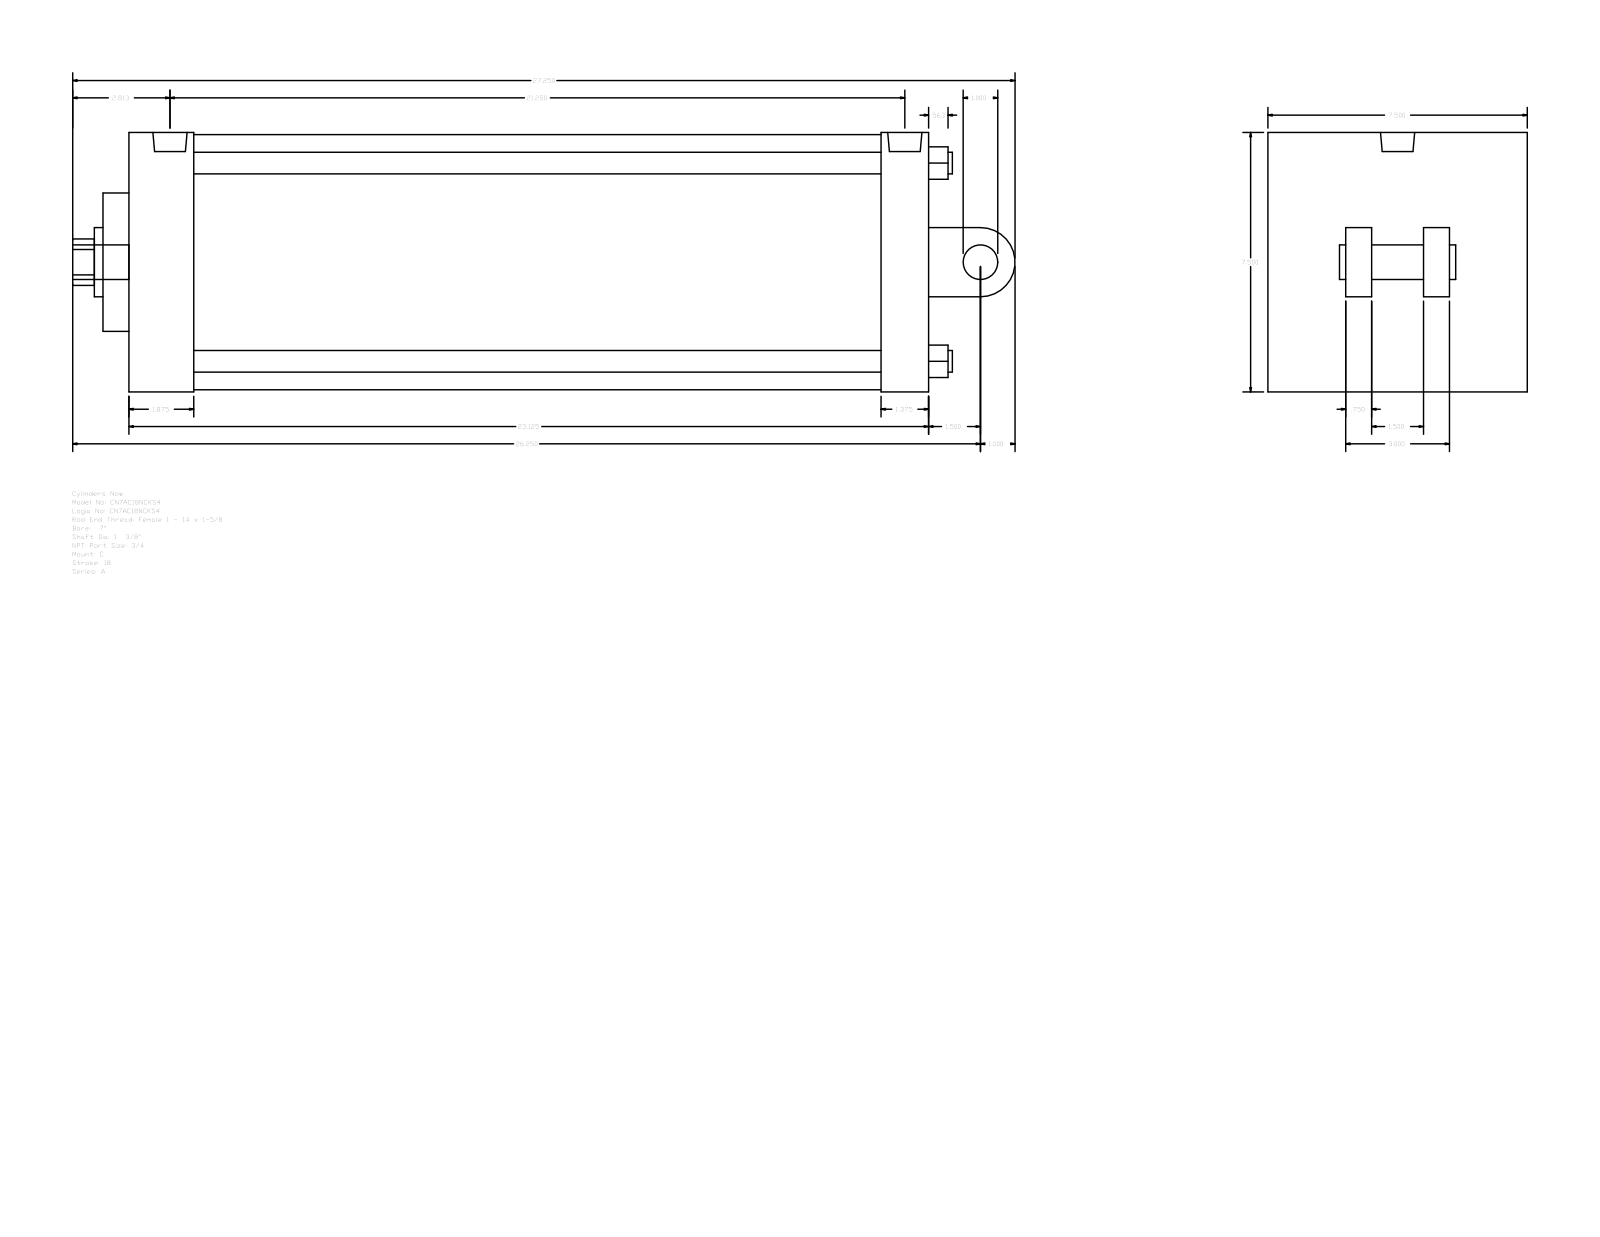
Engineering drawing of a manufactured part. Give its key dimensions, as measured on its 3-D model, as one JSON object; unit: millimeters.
{"part_name": "A_C__0700_1.375", "step_written_by": "GSSL Pune (CONFIG_CONTROL_DESIGN)", "units": "millimeters", "bodies": {"solids": 0, "faces": 104, "planar": 75, "cylindrical": 29, "other": 0}, "overall_size": [692.15, 190.5, 190.5], "round_holes": [[15.88, 4], [15.08, 2], [25.12, 1], [34.92, 1], [50.8, 1], [187.32, 1]], "round_bosses_or_shafts": [[25.4, 2], [15.08, 2], [25.12, 1]], "partial_cylinders_radius": [[17.06, 1], [25.4, 1]], "face_to_face_distances": [190.5, 587.38, 76.2, 57.15, 19.04, 606.42, 66.67, 47.63, 539.75, 571.5], "hole_center_spacings": [102.91, 145.54, 205.82, 5.56]}
